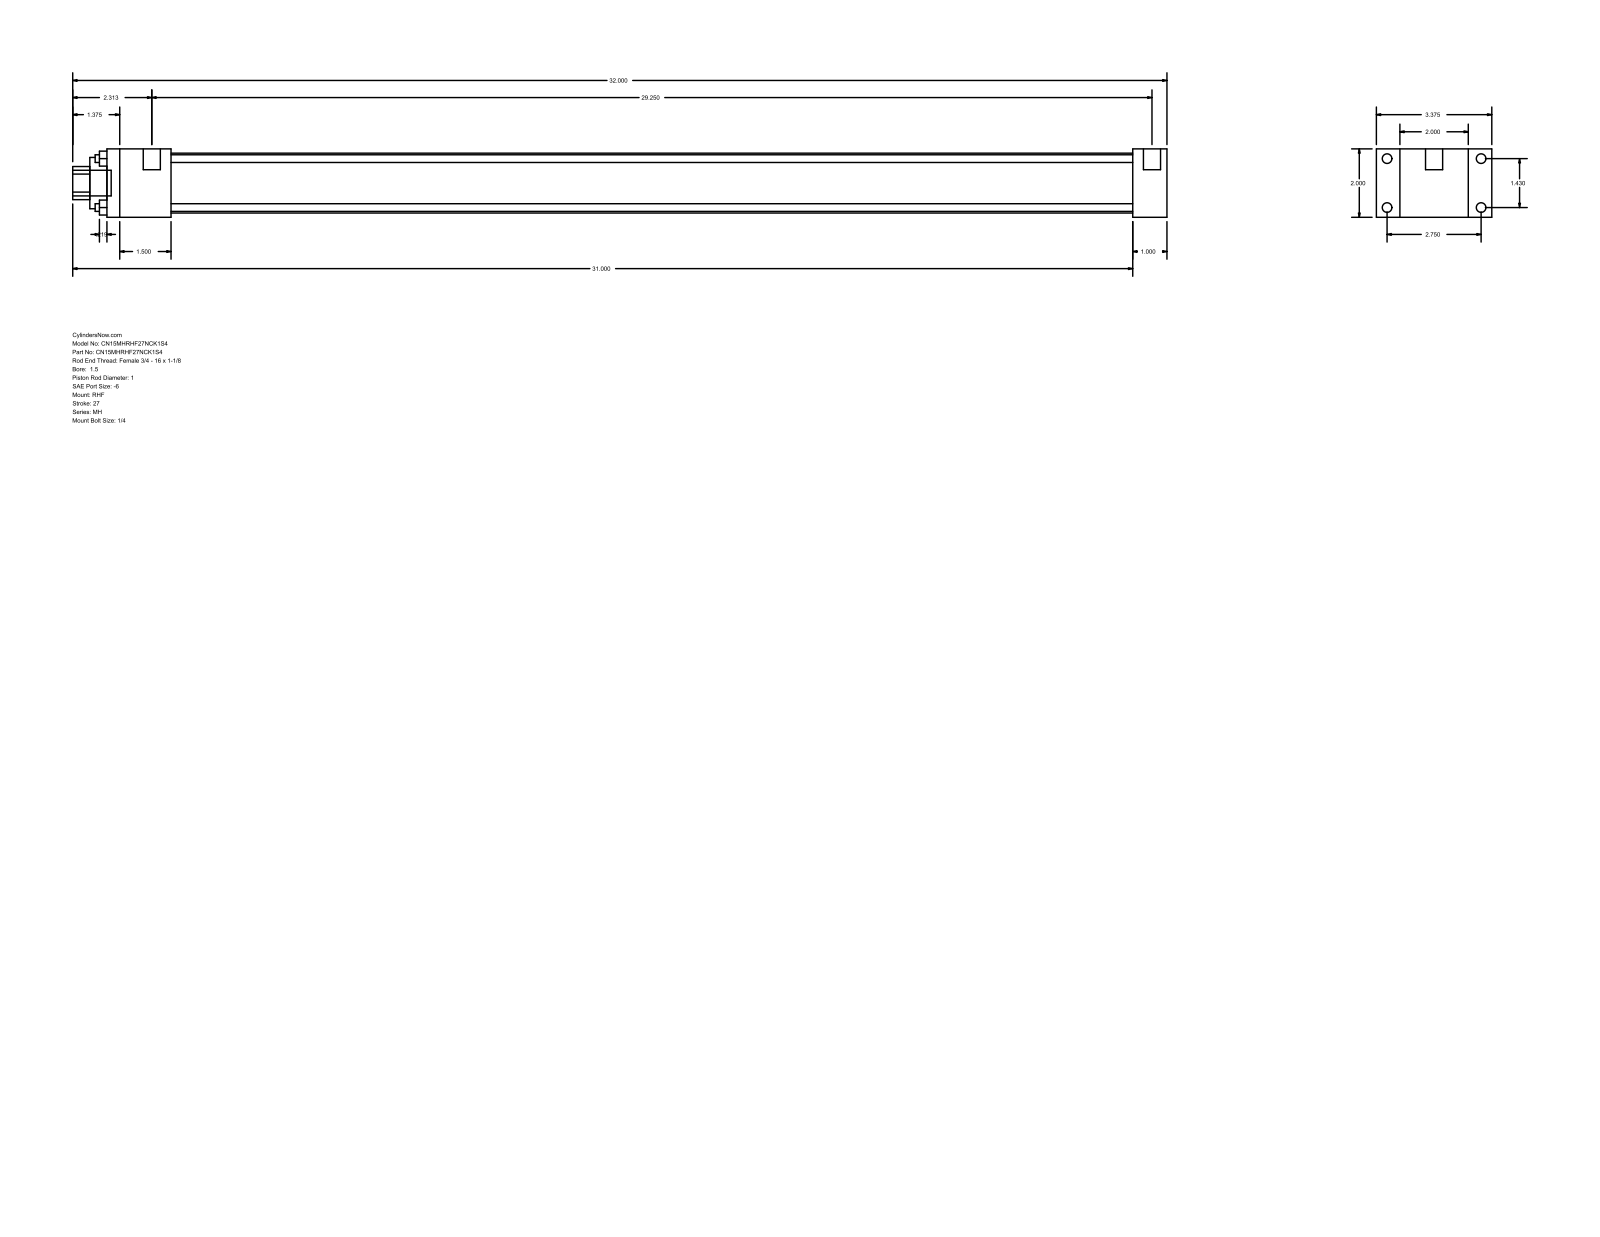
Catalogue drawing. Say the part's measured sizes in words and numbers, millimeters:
The part is named "MH_RHF__0150_1". Its 3-D file was written by "GSSL Pune (CONFIG_CONTROL_DESIGN)". It is 0 solids with 88 faces: 60 planar, 28 cylindrical and 0 other. Overall it measures 812.8 by 85.72 by 50.8 millimeters. Round holes: 4 of diameter 5.71, 1 of diameter 25.4, 1 of diameter 38.1, 1 of diameter 44.45. Round bosses or shafts: 4 of diameter 7.14, 4 of diameter 5.56, 2 of diameter 12.7, 1 of diameter 19.05. Partial cylindrical surfaces (rounded edges, fillets, slot ends): 1 of radius 12.29. The main face-to-face distances are 50.8, 25.4, 17.46, 68.26, 85.72, 787.4, 762, 47.63, 714.37, 739.77. The hole center spacings are 25.68, 36.32, 51.36.
